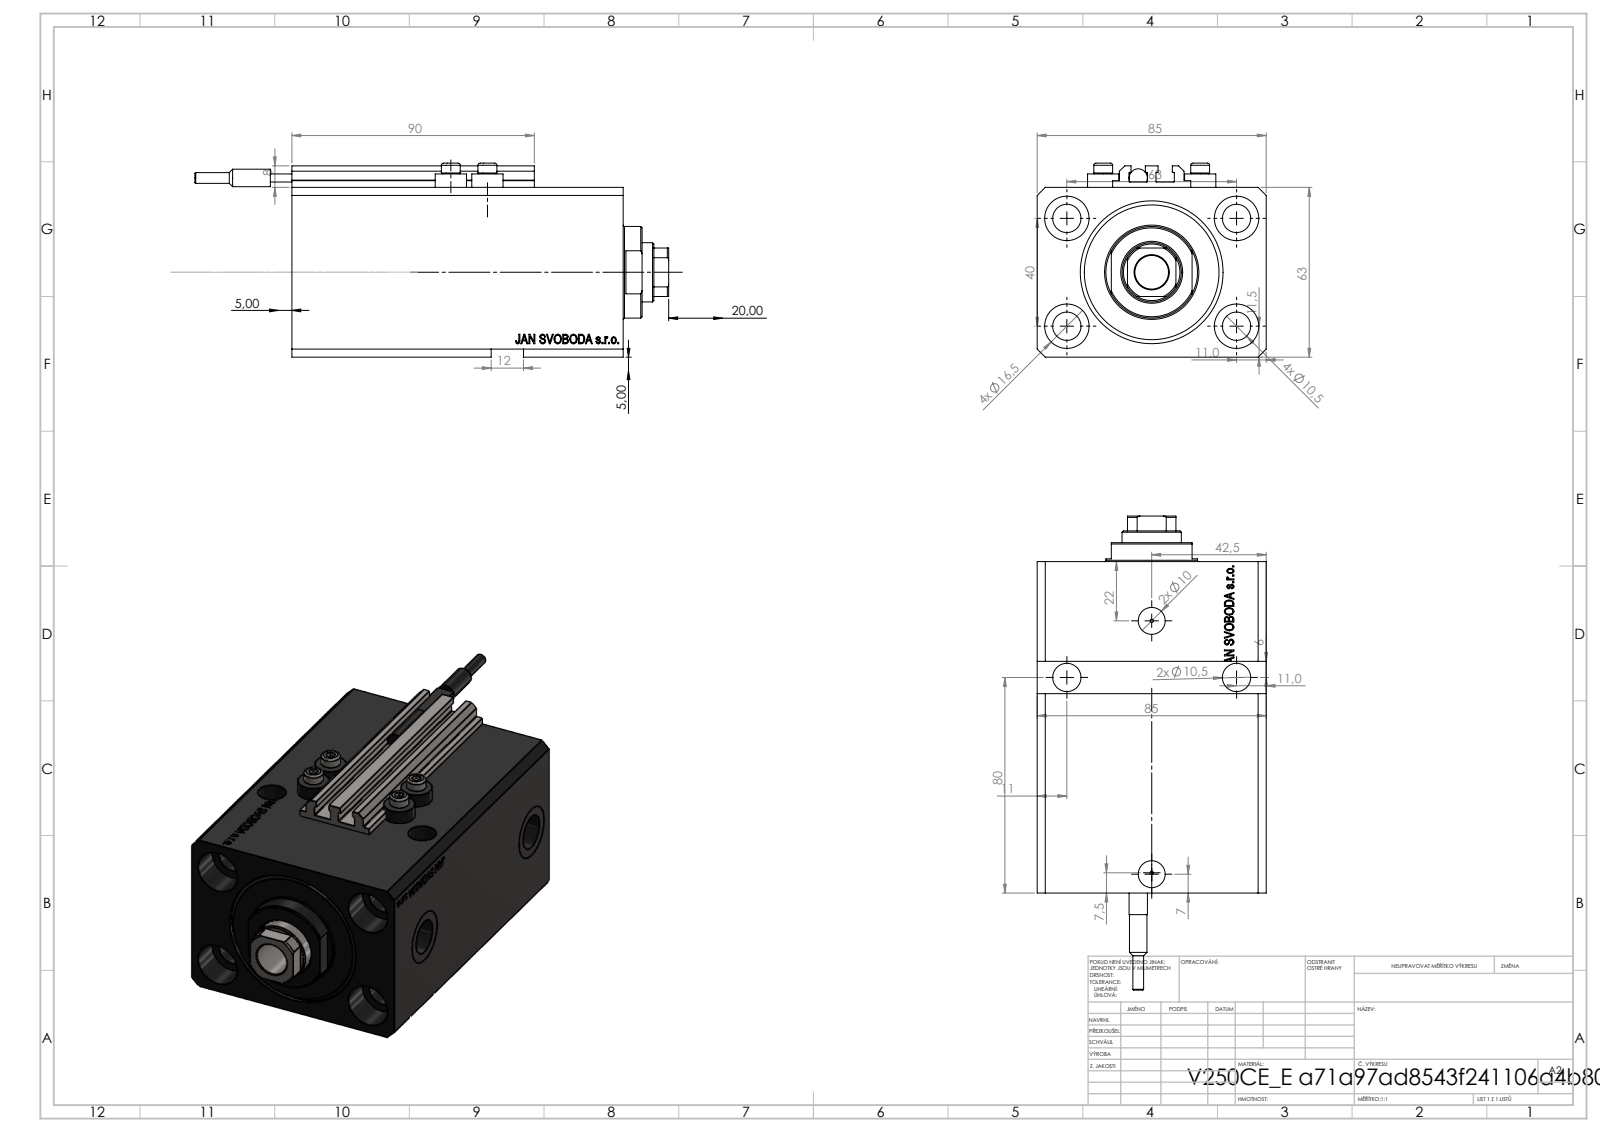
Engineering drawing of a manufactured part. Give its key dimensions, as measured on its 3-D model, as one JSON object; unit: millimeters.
{"part_name": "V250CE_C_VCP; V250CE_E; ALLEN BOLT V250CE; V250CE_VC_E (+1 more)", "step_written_by": "SolidWorks 2019 (CONFIG_CONTROL_DESIGN)", "units": "millimeters", "bodies": {"solids": 9, "faces": 1113, "planar": 551, "cylindrical": 132, "other": 430}, "overall_size": [175.9, 85, 72], "volume_mm3": 566227, "surface_area_mm2": 120819, "round_holes": [[10.5, 6], [1.25, 4], [4, 4], [16.5, 4], [10, 2], [13.16, 2], [20, 2], [12.5, 1], [22, 1], [40, 1], [53, 1]], "round_bosses_or_shafts": [[11.6, 4], [7, 4], [34, 1], [6.8, 1], [6.5, 1], [4, 1]], "partial_cylinders_radius": [[0.2, 10], [10.5, 1]], "face_to_face_distances": [63, 85, 123, 95.9, 27.1, 11.4, 84.5, 111.6, 3, 65], "hole_center_spacings": [37.31, 63, 13.6, 15.4, 24.96, 33.62, 36, 37.86]}
